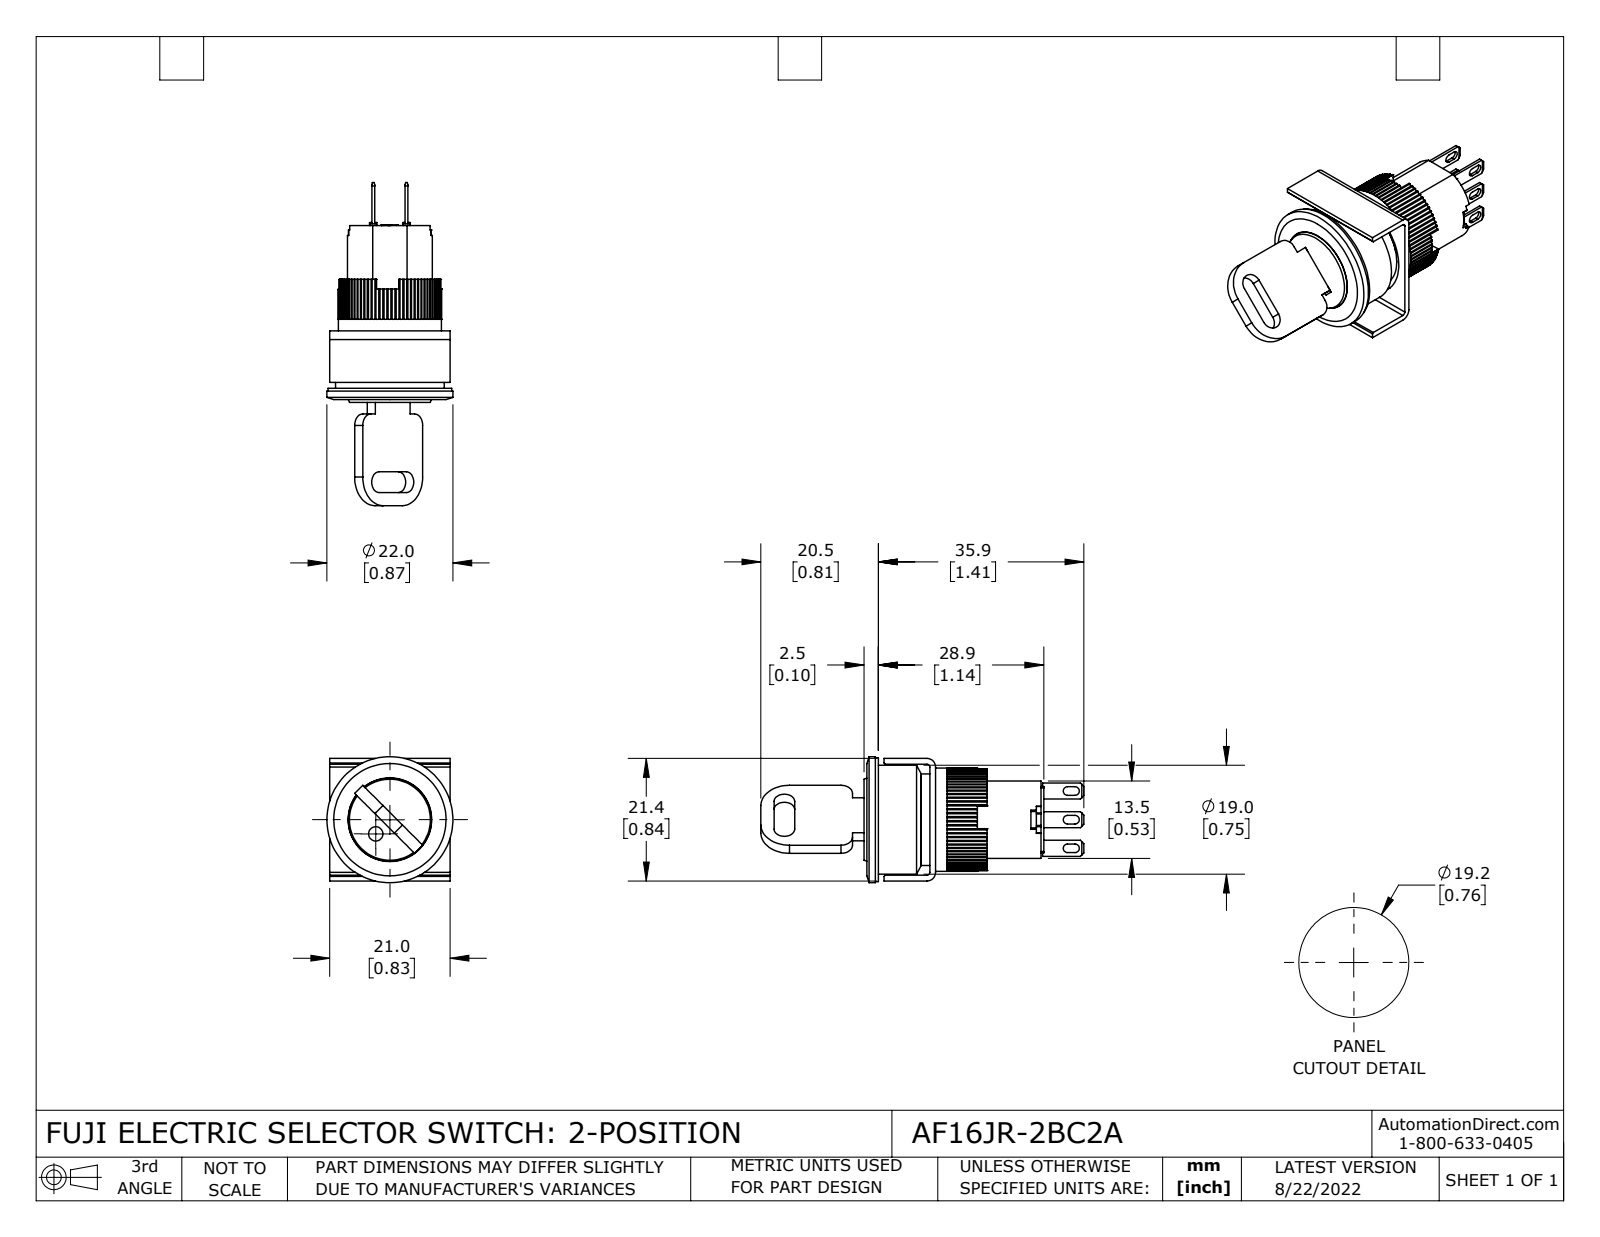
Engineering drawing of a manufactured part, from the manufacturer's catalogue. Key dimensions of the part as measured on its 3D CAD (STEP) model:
Part name (STEP PRODUCT): AF16JR-2BC2A
STEP written by: SolidWorks 2021 (CONFIG_CONTROL_DESIGN)
Units: inches
Bodies: 13 solids, 707 faces (518 planar, 183 cylindrical, 6 other)
Overall size (bounding box): 2.22 × 0.866 × 0.866
Volume: 0.495 in³ · Surface area: 11.24 in²
Round holes (diameter × count): ⌀0.039 ×1, ⌀0.098 ×1, ⌀0.575 ×1, ⌀0.709 ×1, ⌀0.748 ×1
Round bosses / shafts (diameter × count): ⌀0.866 ×1, ⌀0.85 ×1, ⌀0.63 ×1, ⌀0.583 ×1, ⌀0.571 ×1
Partial cylindrical surfaces — rounded edges, fillets, slot ends (radius × count): R0.01 ×80, R0.008 ×12, R0.03 ×6, R0.02 ×2, R0.059 ×2, R0.071 ×2, R0.079 ×2, R0.197 ×2
Main face-to-face distances: 0.079, 0.039, 0.02, 0.374, 0.177, 0.394, 0.803, 0.098, 0.059, 0.764
Hole centre spacings: 0.137
